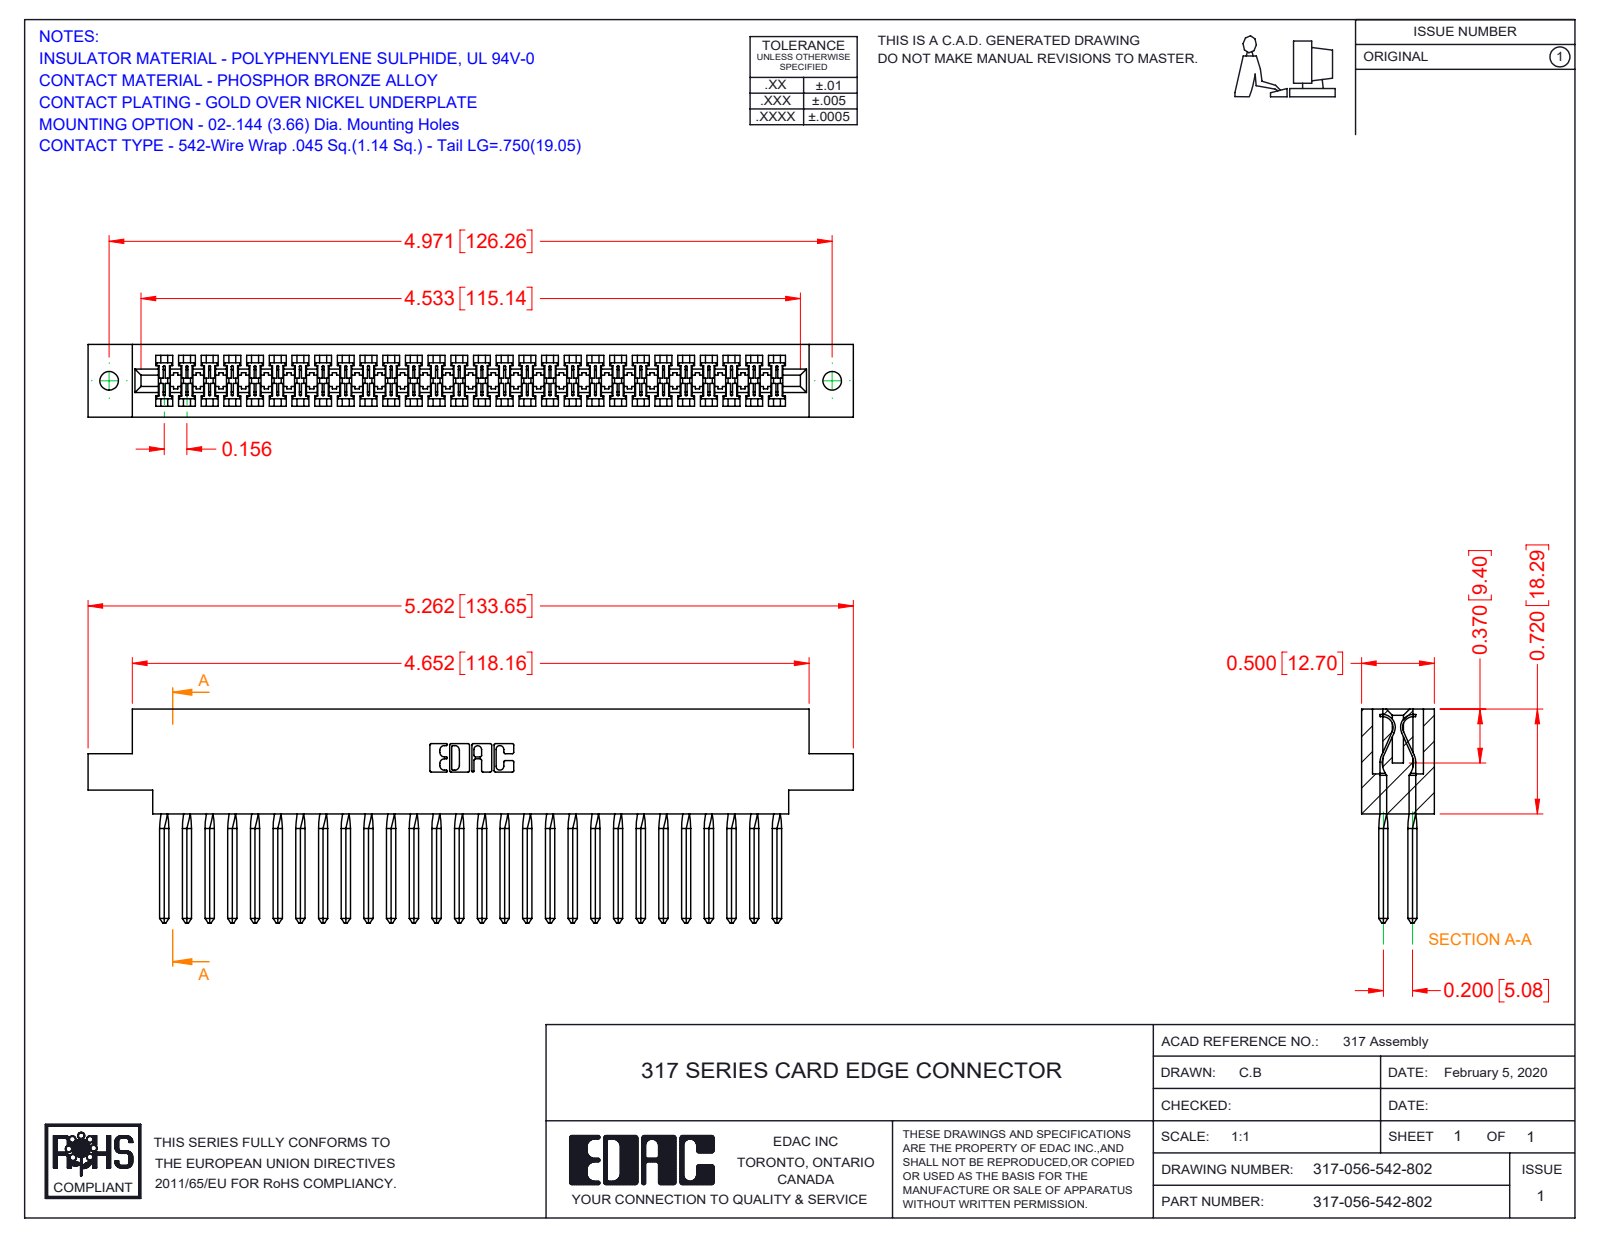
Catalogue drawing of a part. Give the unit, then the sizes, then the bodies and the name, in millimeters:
Units: millimetres
Overall size (bounding box): 133.7 × 37.3 × 12.7
Round holes (diameter × count): ⌀3.3 ×2
Partial cylindrical surfaces — rounded edges, fillets, slot ends (radius × count): R0.2 ×112, R0.3 ×22, R0.2 ×6, R0.8 ×6, R0.7 ×3, R1.9 ×2, R2.3 ×2, R2.5 ×2
Main face-to-face distances: 12.7, 1.9, 10.8, 8.9, 5.1, 2.8, 2.9, 1.2, 3.3, 9.4
Hole centre spacings: 126.3
Volume: 21 400 mm³ · Surface area: 29 050 mm²
Bodies: 57 solids, 3294 faces (2634 planar, 436 cylindrical, 224 other)
Part name (STEP PRODUCT): 317-056-542-802; 317-290-003_542; 317 Part_.144 Dia
STEP written by: SolidWorks 2016 (CONFIG_CONTROL_DESIGN)
